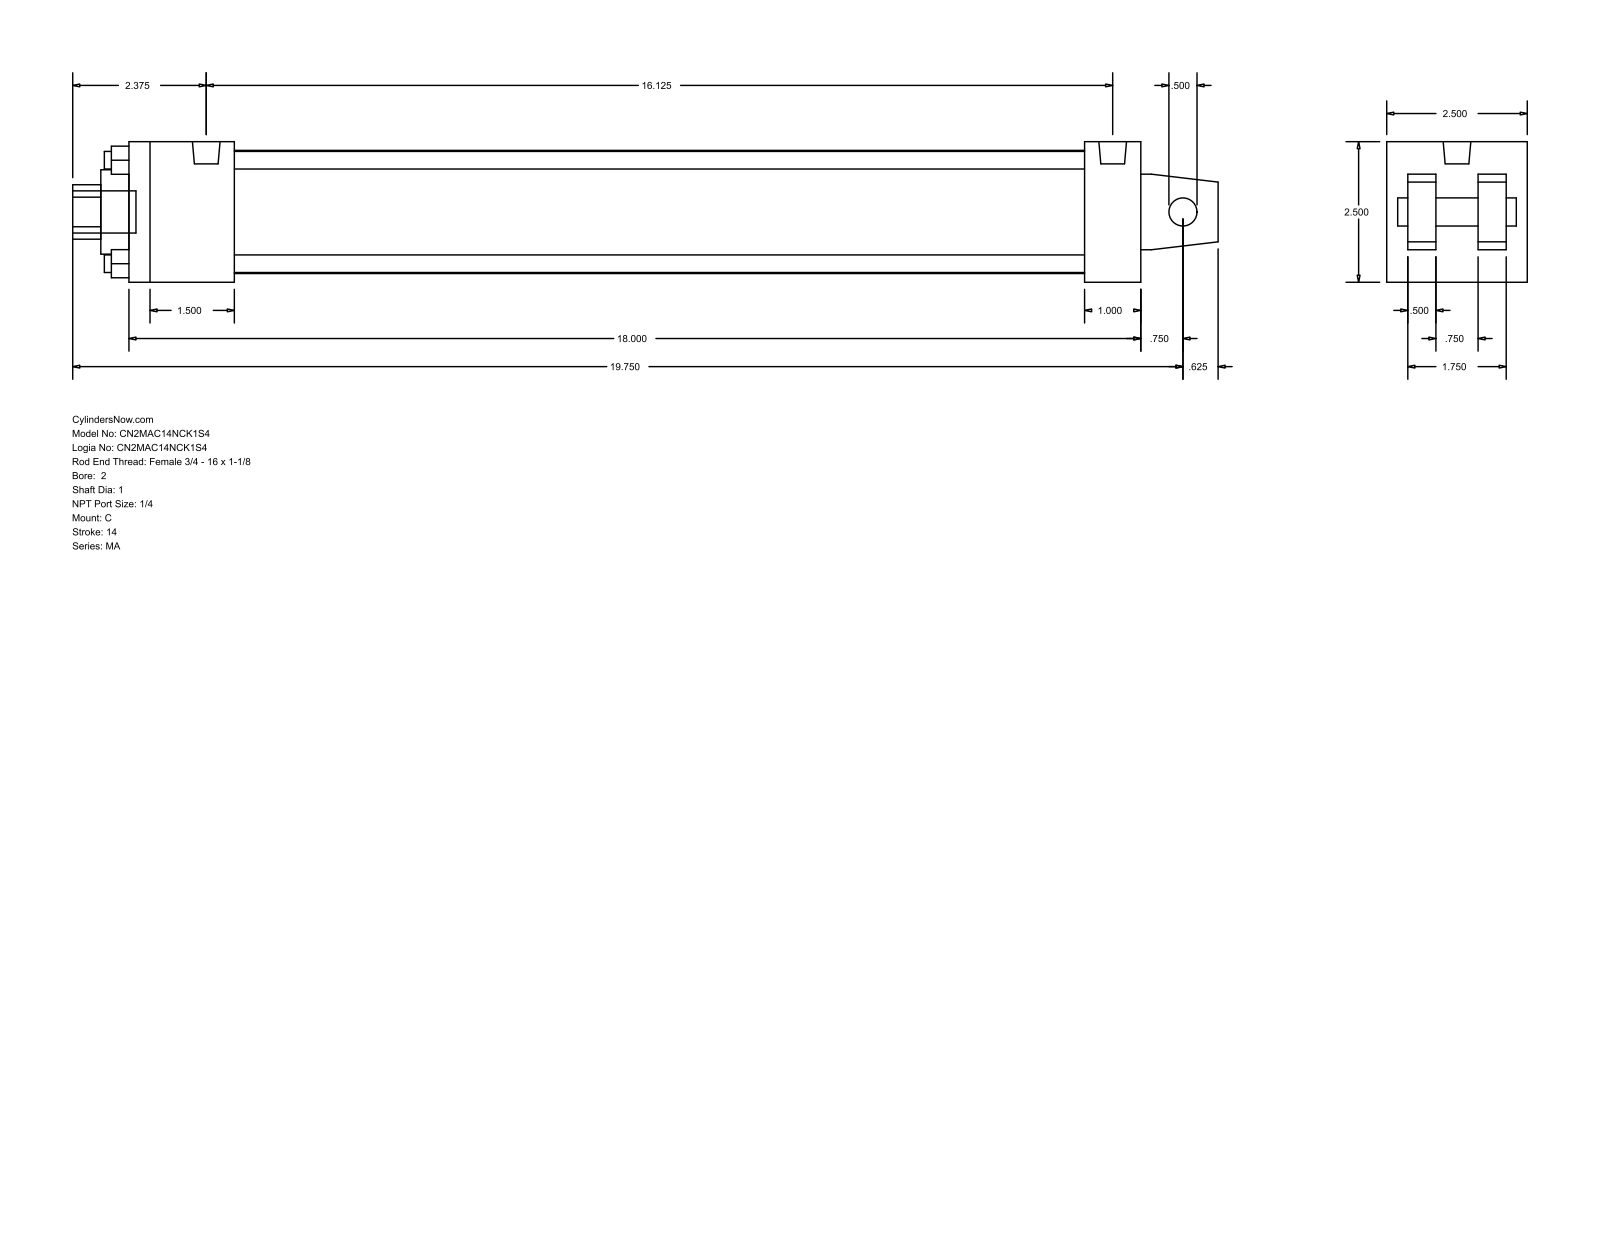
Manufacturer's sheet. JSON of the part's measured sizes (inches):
{"part_name": "MA_C__0200_1", "step_written_by": "GSSL Pune (CONFIG_CONTROL_DESIGN)", "units": "inches", "bodies": {"solids": 0, "faces": 103, "planar": 76, "cylindrical": 27, "other": 0}, "overall_size": [20.375, 2.5, 2.5], "round_holes": [[0.313, 4], [0.5, 1], [1, 1], [1.5, 1], [2.19, 1]], "round_bosses_or_shafts": [[0.313, 4], [0.492, 2], [0.75, 1]], "partial_cylinders_radius": [[0.484, 1]], "face_to_face_distances": [2.5, 0.5, 18, 0.875, 1.625, 0.375, 2.125, 1.25, 1.875, 1], "hole_center_spacings": [1.301, 1.84, 2.602]}
